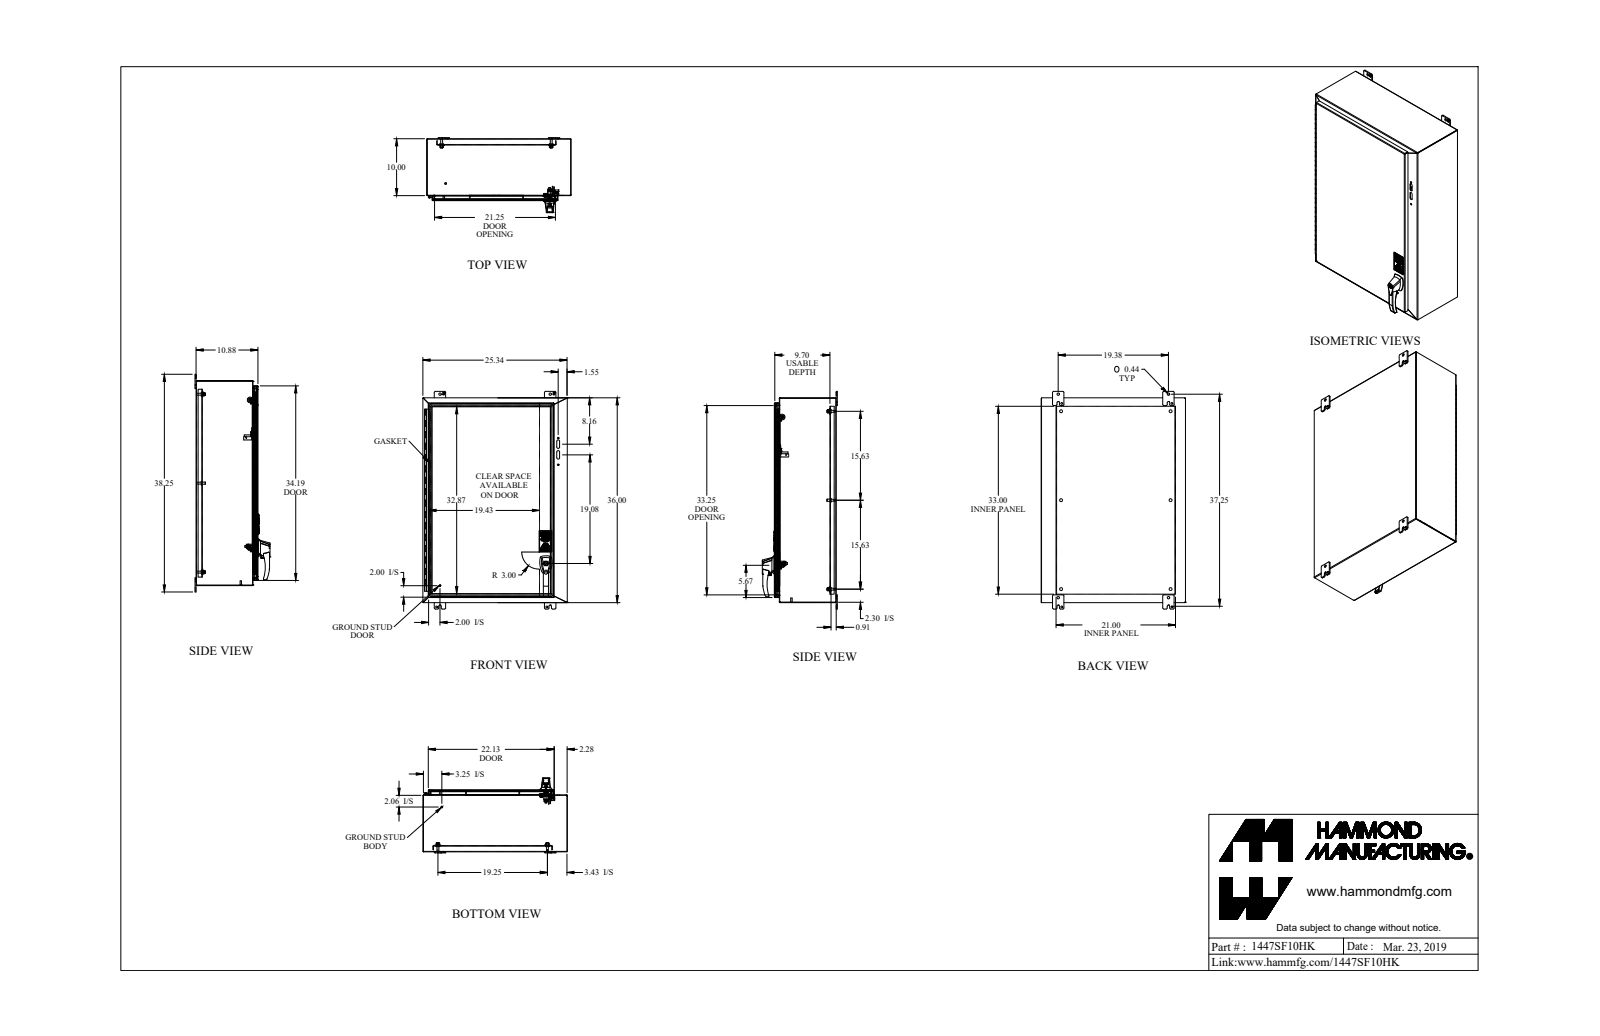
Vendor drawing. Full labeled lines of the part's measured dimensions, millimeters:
Part name (STEP PRODUCT): 1447SF10HK
STEP written by: SolidWorks 2019 (AUTOMOTIVE_DESIGN)
Units: millimetres
Bodies: 55 solids, 1279 faces (787 planar, 369 cylindrical, 123 other)
Overall size (bounding box): 971.54 × 644.53 × 334.7
Volume: 5 575 000 mm³ · Surface area: 5 555 000 mm²
Round holes (diameter × count): ⌀12.7 ×6, ⌀7.94 ×5, ⌀4.47 ×4, ⌀7.81 ×4, ⌀11.11 ×4, ⌀11.3 ×4, ⌀3.97 ×2, ⌀4.39 ×2, ⌀5.46 ×2, ⌀6.35 ×2, ⌀6.73 ×2, ⌀7.14 ×2
Round bosses / shafts (diameter × count): ⌀9.53 ×10, ⌀6.35 ×7, ⌀25.4 ×6, ⌀16.51 ×6, ⌀8.38 ×6, ⌀3.97 ×4, ⌀12.7 ×2, ⌀10.21 ×2
Partial cylindrical surfaces — rounded edges, fillets, slot ends (radius × count): R2 ×28, R4.76 ×24, R0.17 ×16, R6.35 ×12, R3.17 ×11, R0.76 ×8, R3.83 ×8, R5.54 ×8
Main face-to-face distances: 1.83, 274.4, 272.57, 276.23, 2.41, 642.7, 248.19, 246.36, 26.21, 28.04
Hole centre spacings: 488.95, 396.88, 492.13, 629.75, 1032.83, 28.21, 44.08, 44.09
